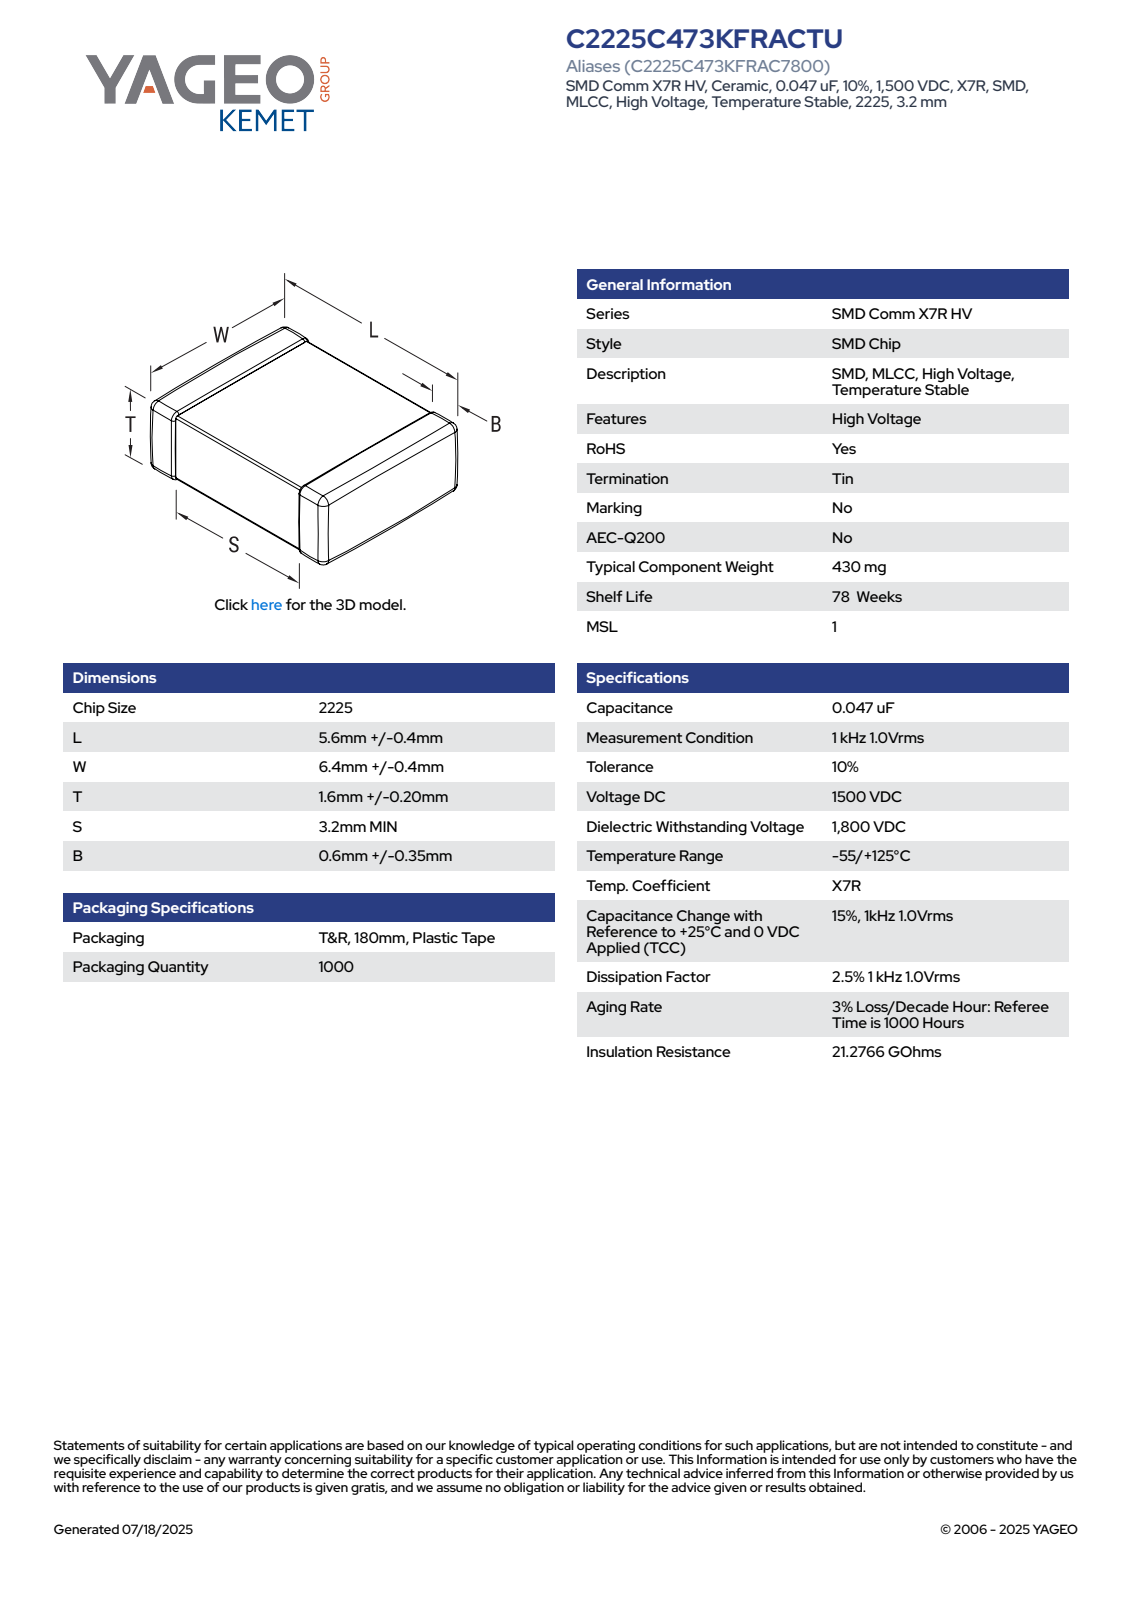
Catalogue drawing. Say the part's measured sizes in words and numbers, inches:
The part is named "CCS_CCSTDNOS_2225_L6W6.8T1.8B0.95". Its 3-D file was written by "SolidWorks 2014 (AUTOMOTIVE_DESIGN)". It is 4 solids with 125 faces: 71 planar, 38 cylindrical and 16 other. Overall it measures 0.268 by 0.236 by 0.071 inches. Its volume is 0.004 cubic inches and its surface area 0.191 square inches. Partial cylindrical surfaces (rounded edges, fillets, slot ends): 24 of radius 0.006. The main face-to-face distances are 0.06, 0.065, 0.236, 0.071, 0.257, 0.262, 0.268, 0.131, 0.017, 0.137.
